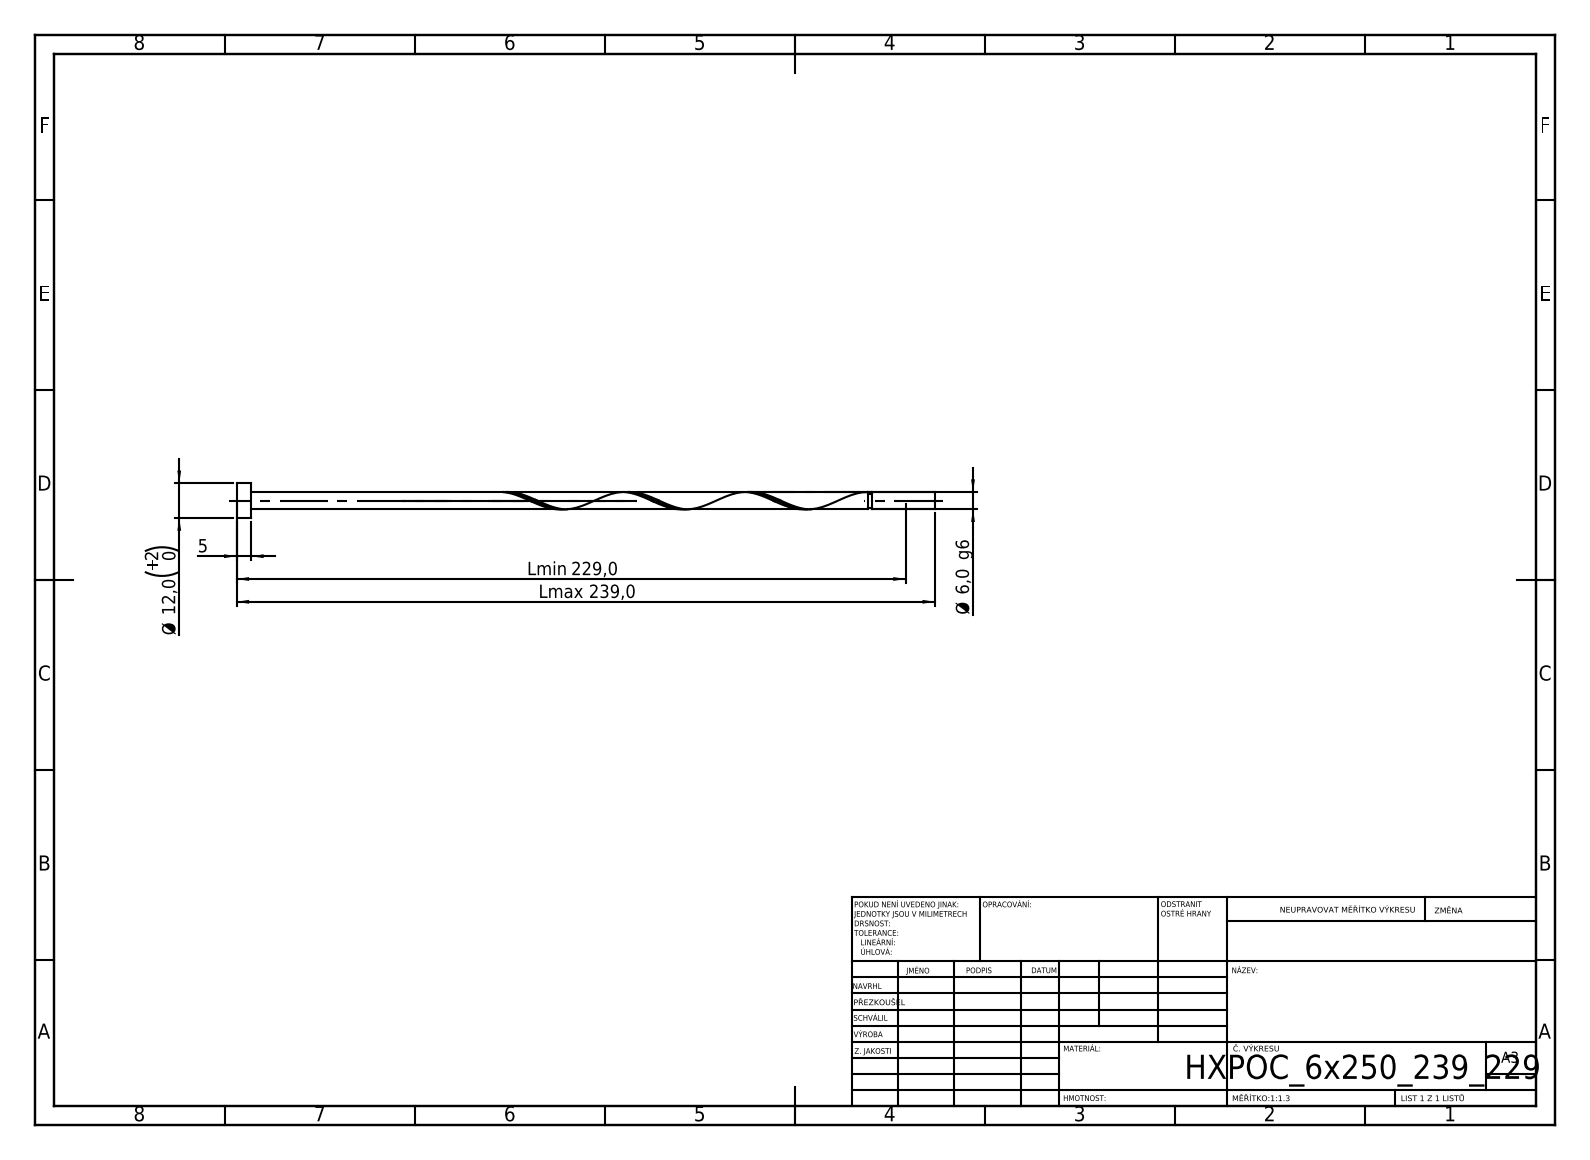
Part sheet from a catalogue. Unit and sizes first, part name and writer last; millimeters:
Units: millimetres
Overall size (bounding box): 239 × 12 × 12
Round bosses / shafts (diameter × count): ⌀12 ×1, ⌀6 ×1, ⌀4.8 ×1
Main face-to-face distances: 5, 239, 234, 217.4, 212.4, 21.6, 216.2, 211.2, 1.2, 22.8
Volume: 7 102 mm³ · Surface area: 4 922 mm²
Bodies: 1 solid, 21 faces (6 planar, 14 cylindrical, 1 other)
STEP written by: SolidWorks 2019 (CONFIG_CONTROL_DESIGN)
